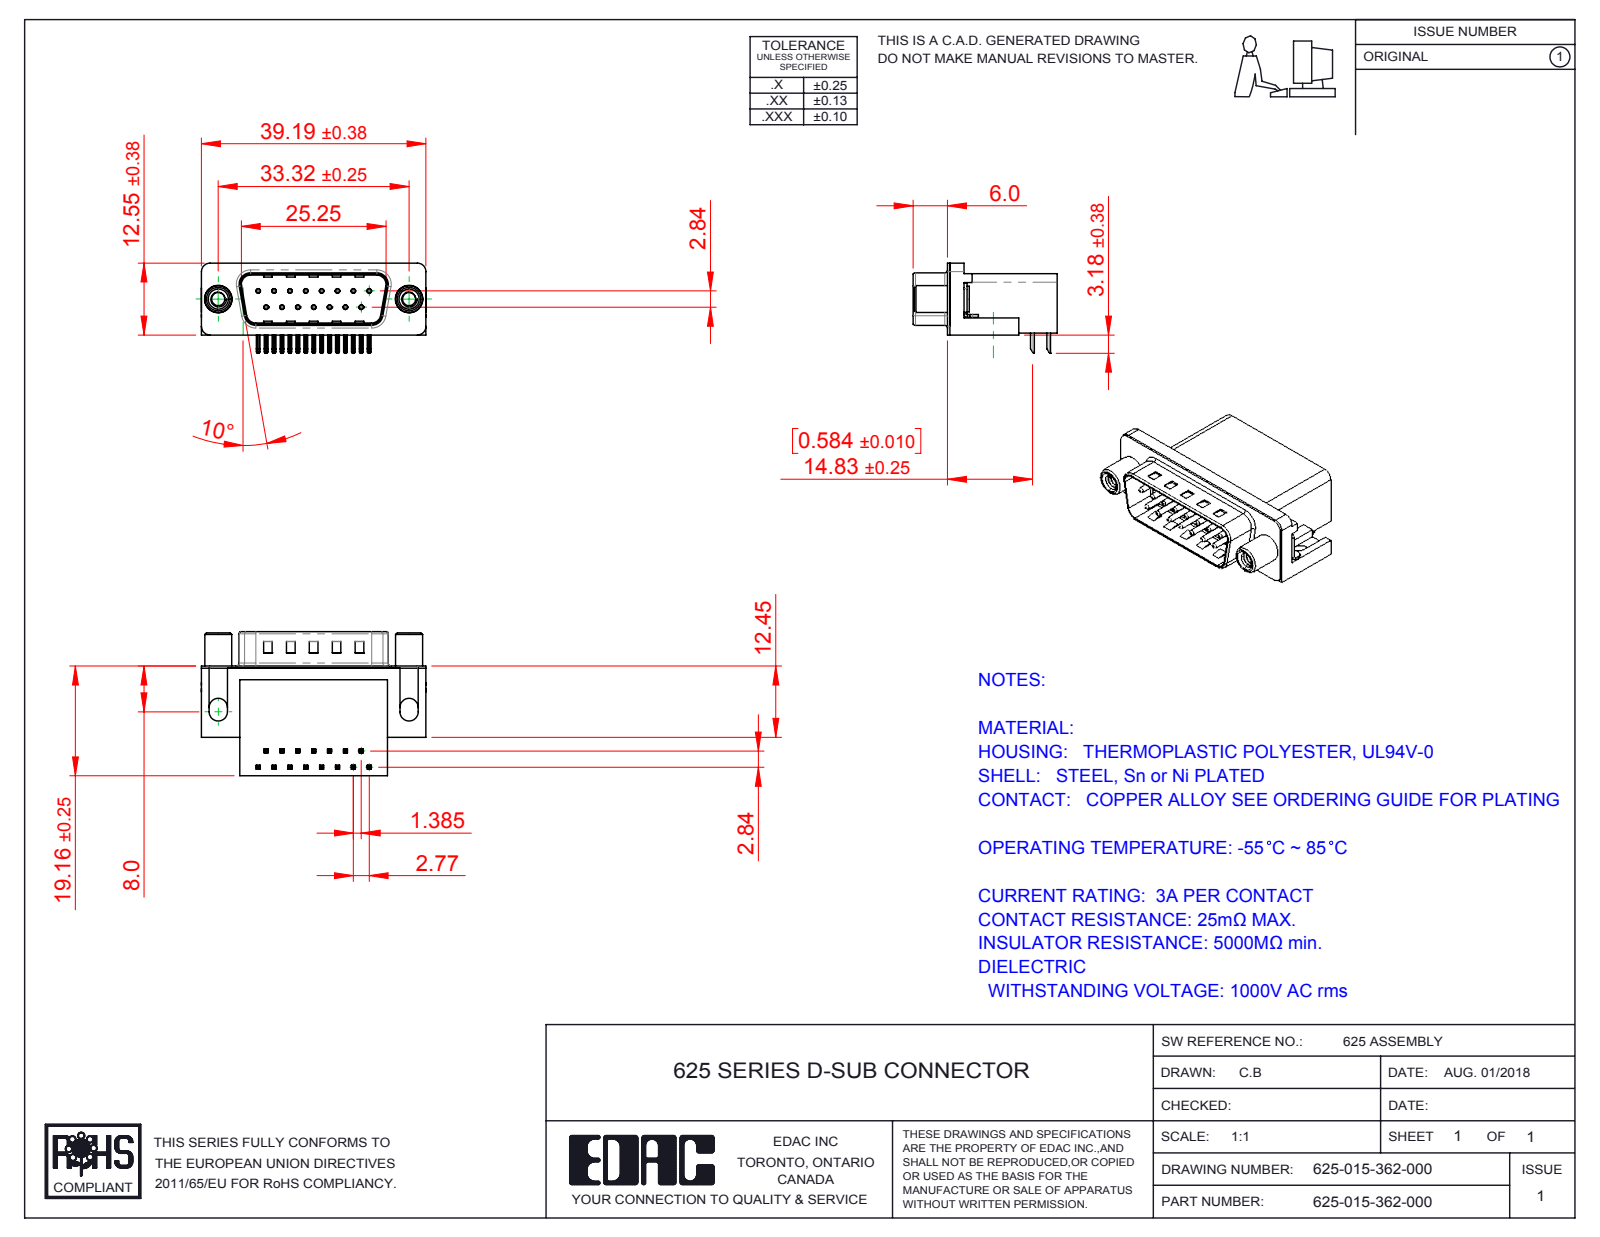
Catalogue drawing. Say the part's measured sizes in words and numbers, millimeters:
The part is named "625-015-362-000; 625 Shell_15 Socket; 625 Housing_15 Socket; 625 Contact Top (+3 more)". Its 3-D file was written by "SolidWorks 2016 (CONFIG_CONTROL_DESIGN)". It is 21 solids with 1471 faces: 887 planar, 451 cylindrical and 133 other. Overall it measures 39.22 by 25.16 by 15.73 millimeters. Its volume is 6 306 cubic millimeters and its surface area 6 490 square millimeters. Round holes: 15 of diameter 0.35, 15 of diameter 0.8, 2 of diameter 2.3, 2 of diameter 3.1, 2 of diameter 4, 2 of diameter 4.8, 2 of diameter 5. Round bosses or shafts: 15 of diameter 0.75, 2 of diameter 4.9, 2 of diameter 4.7, 2 of diameter 4.5, 2 of diameter 3.85. Partial cylindrical surfaces (rounded edges, fillets, slot ends): 60 of radius 0.25, 30 of radius 0.12, 16 of radius 1, 9 of radius 0.5, 8 of radius 1.6, 6 of radius 1.5, 4 of radius 0.9, 4 of radius 2. The main face-to-face distances are 0.4, 10.35, 18.76, 2.1, 10.46, 1.7, 10.86, 19.16, 8.76, 16.26. The hole center spacings are 3.16, 2.77, 5.54, 8.31, 11.08, 5.03, 5.04, 7.48.
